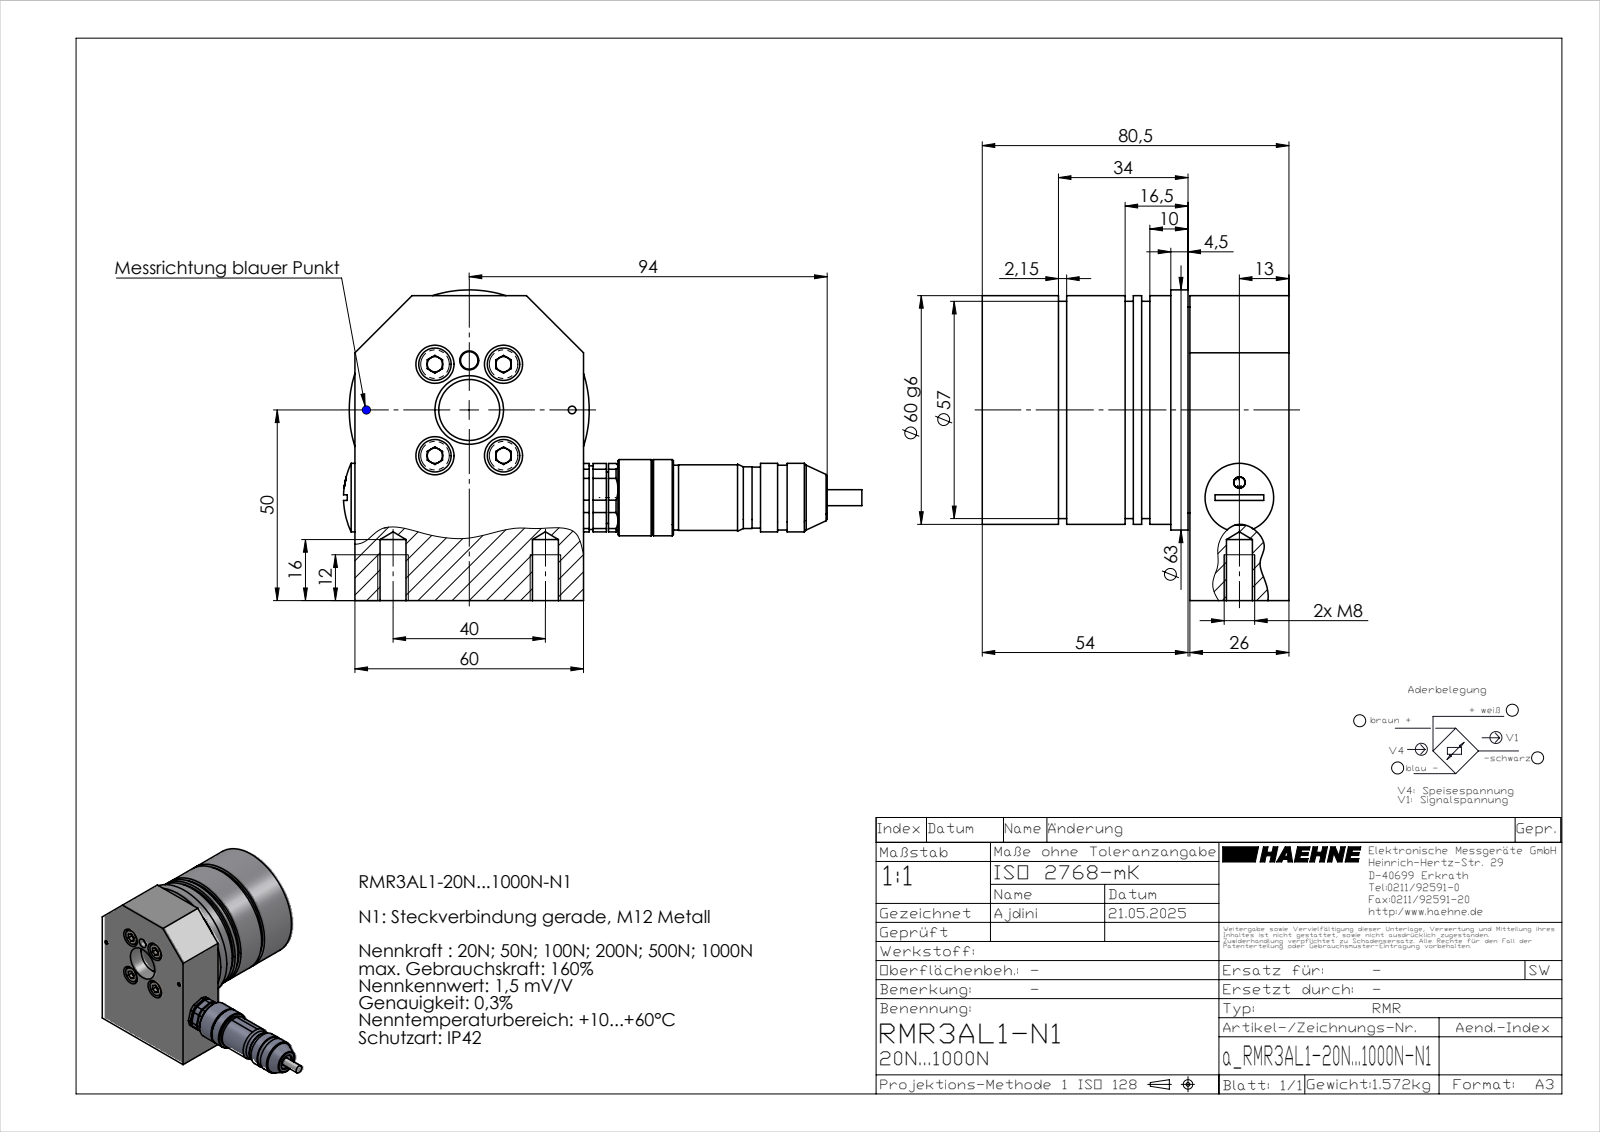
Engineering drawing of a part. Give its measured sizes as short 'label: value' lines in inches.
name: a_RMR3AL1-20N...1000N-N1
written by: SolidWorks 2023 (AUTOMOTIVE_DESIGN)
unit: in
bodies: 16 solids, 491 faces (248 planar, 156 cylindrical, 87 other)
size: 5.356 × 3.209 × 3.169
volume: 14.85 in³; area: 116 in²
holes: 5× ⌀0.039, 4× ⌀0.165, 4× ⌀0.209, 4× ⌀0.394, 2× ⌀0.079, 2× ⌀0.268, 1× ⌀0.025, 1× ⌀0.118, 1× ⌀0.177, 1× ⌀0.197, 1× ⌀0.323, 1× ⌀0.33
bosses: 5× ⌀0.034, 4× ⌀0.335, 4× ⌀0.197, 4× ⌀0.059, 4× ⌀0.039, 1× ⌀2.48, 1× ⌀2.362, 1× ⌀2.244
rounds: 6× R0.012, 4× R0.039, 1× R0.022, 1× R0.024, 1× R0.03, 1× R0.138, 1× R0.945, 1× R1.575
face distances: 0.453, 1.909, 1.457, 2.874, 2.146, 2.441, 0.433, 1.85, 0.591, 1.024
hole spacings: 0.098, 0.139, 0.591, 0.852, 1.494, 0.197, 0.357, 0.709
